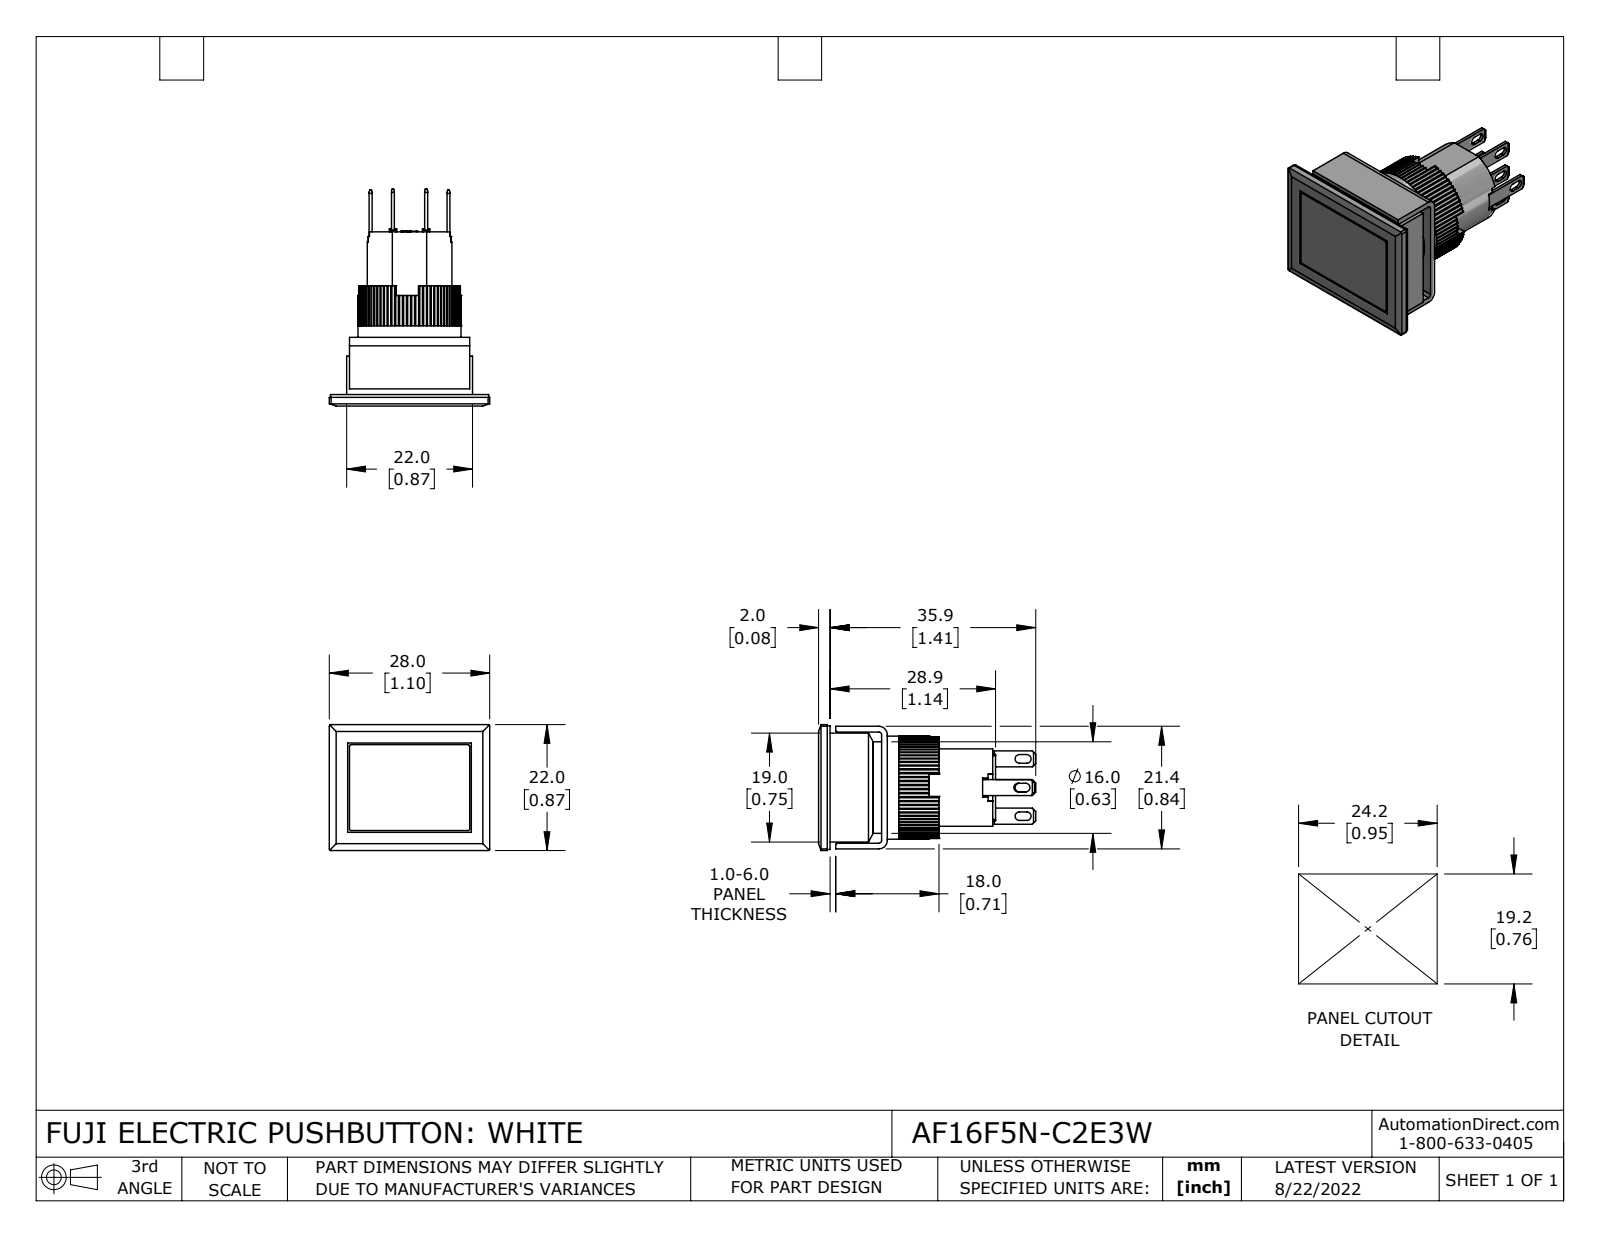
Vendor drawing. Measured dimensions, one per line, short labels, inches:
name: AF16F5N-C2E3W
written by: SolidWorks 2021 (CONFIG_CONTROL_DESIGN)
unit: in
bodies: 14 solids, 828 faces (644 planar, 182 cylindrical, 2 other)
size: 1.492 × 1.102 × 0.866
volume: 0.543 in³; area: 12.03 in²
holes: 1× ⌀0.039, 1× ⌀0.709
bosses: 1× ⌀0.63, 1× ⌀0.583
rounds: 80× R0.01, 12× R0.008, 8× R0.012, 8× R0.03, 2× R0.02, 2× R0.059
face distances: 0.374, 0.059, 0.02, 0.142, 0.039, 0.315, 0.232, 0.083, 0.079, 0.756
